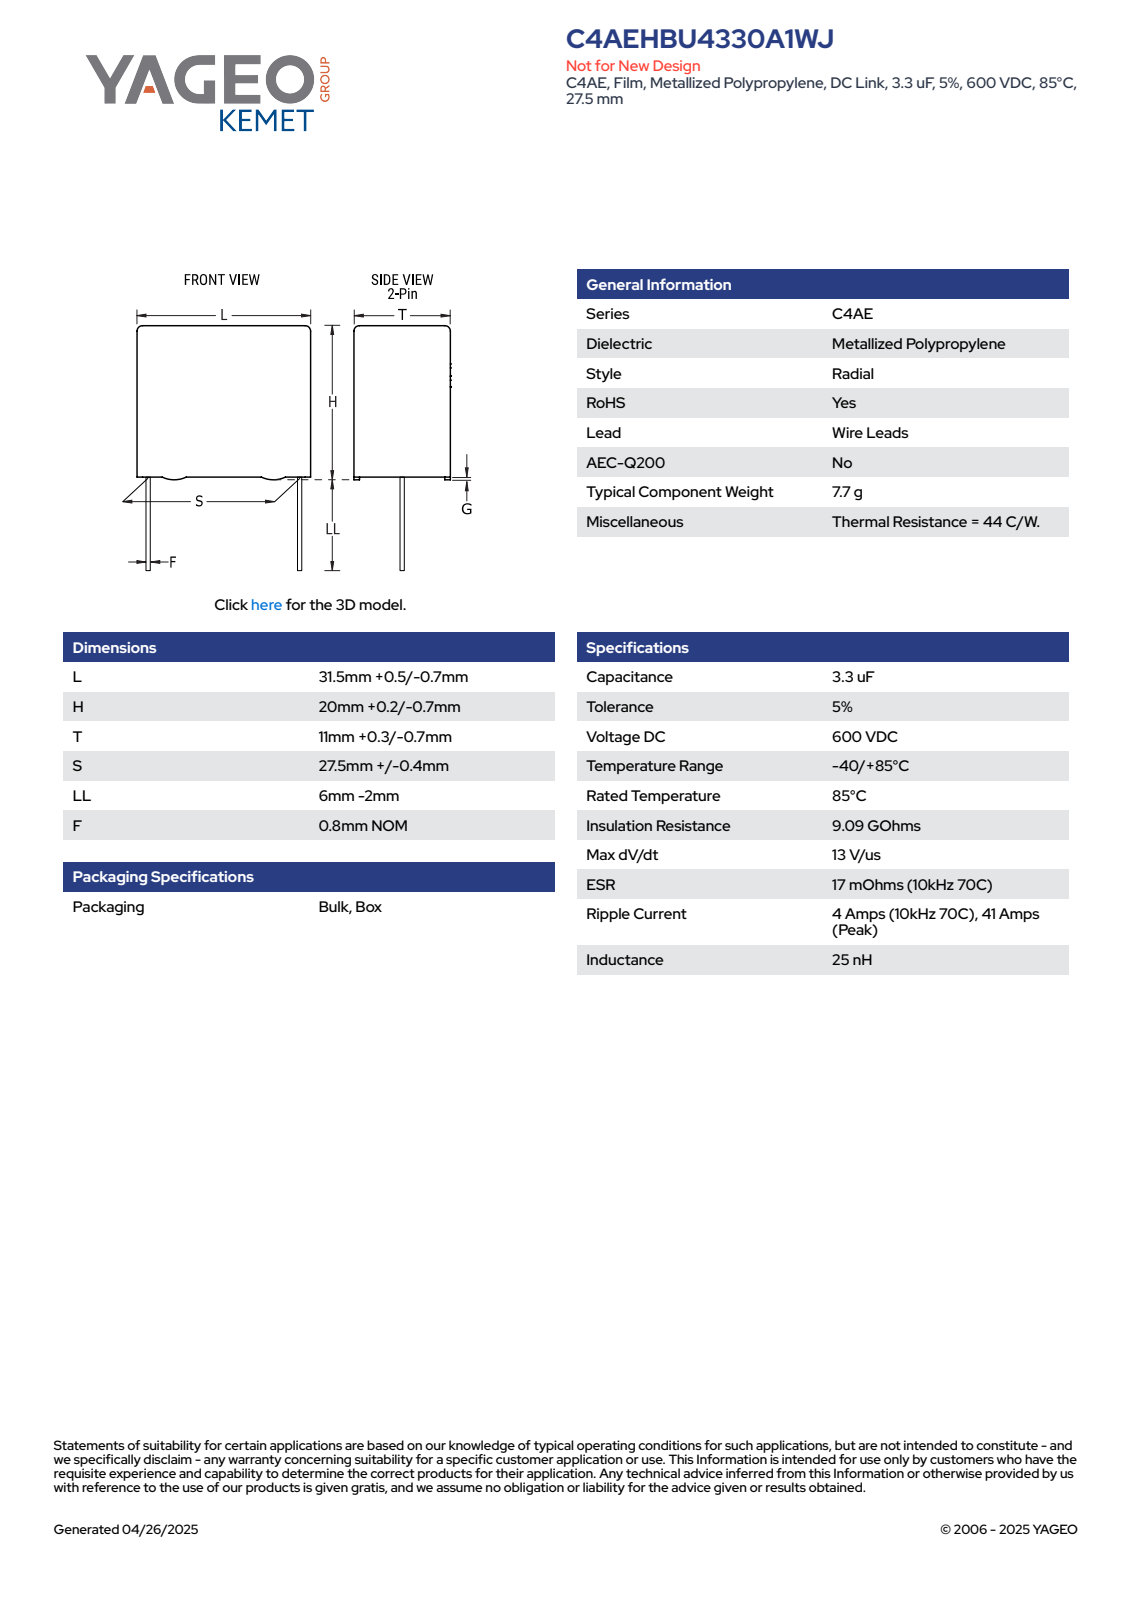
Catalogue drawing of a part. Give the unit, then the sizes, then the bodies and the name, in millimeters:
Units: millimetres
Overall size (bounding box): 32 × 24.2 × 11.3
Round bosses / shafts (diameter × count): ⌀0.8 ×2
Partial cylindrical surfaces — rounded edges, fillets, slot ends (radius × count): R0.5 ×4
Main face-to-face distances: 11.3, 19.7, 32, 0.5, 20.2, 1, 10.3, 9.3, 18.78, 4
Volume: 7 134 mm³ · Surface area: 2 554 mm²
Bodies: 4 solids, 89 faces (81 planar, 8 cylindrical, 0 other)
Part name (STEP PRODUCT): CFP_RBG_31.5X20X11_L32H20.2T11.3S27.9LL4F0.8G0.5
STEP written by: SolidWorks 2014 (AUTOMOTIVE_DESIGN)
